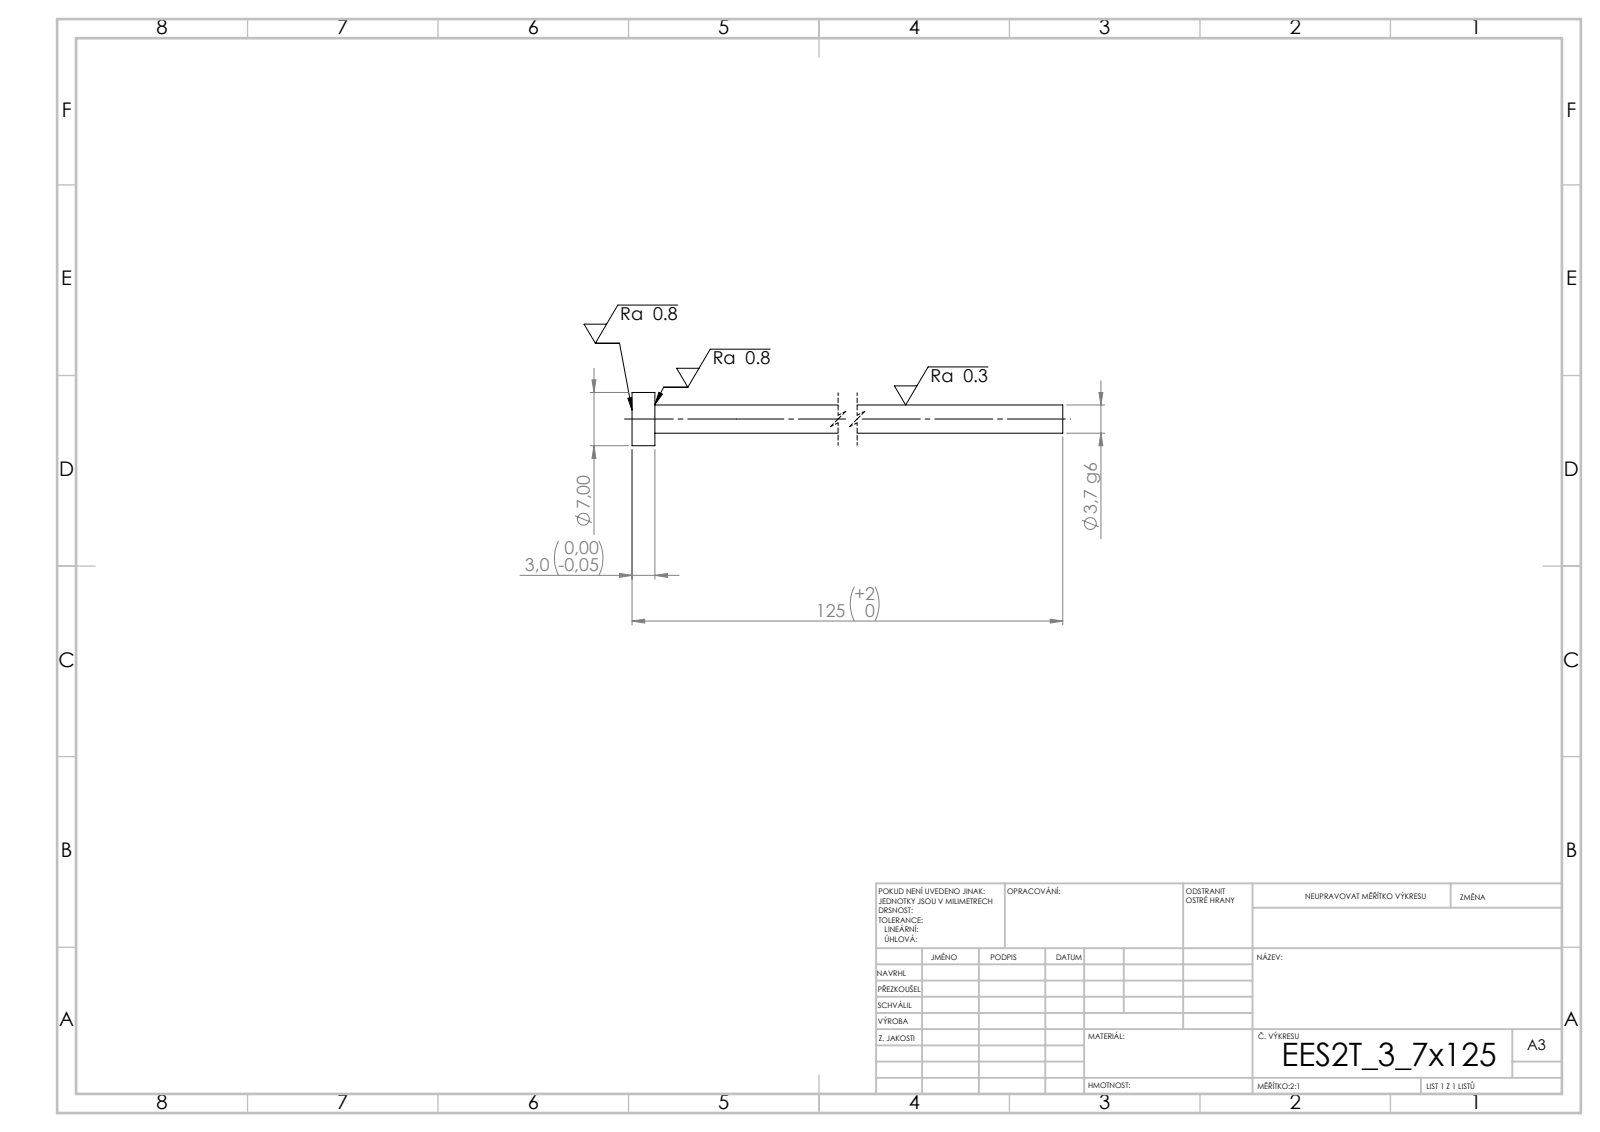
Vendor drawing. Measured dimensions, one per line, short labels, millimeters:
written by: SolidWorks 2019 (CONFIG_CONTROL_DESIGN)
unit: mm
bodies: 1 solid, 7 faces (3 planar, 4 cylindrical, 0 other)
size: 125 × 7 × 7
volume: 1 427 mm³; area: 1 561 mm²
bosses: 1× ⌀7, 1× ⌀3.7
face distances: 3, 125, 122
